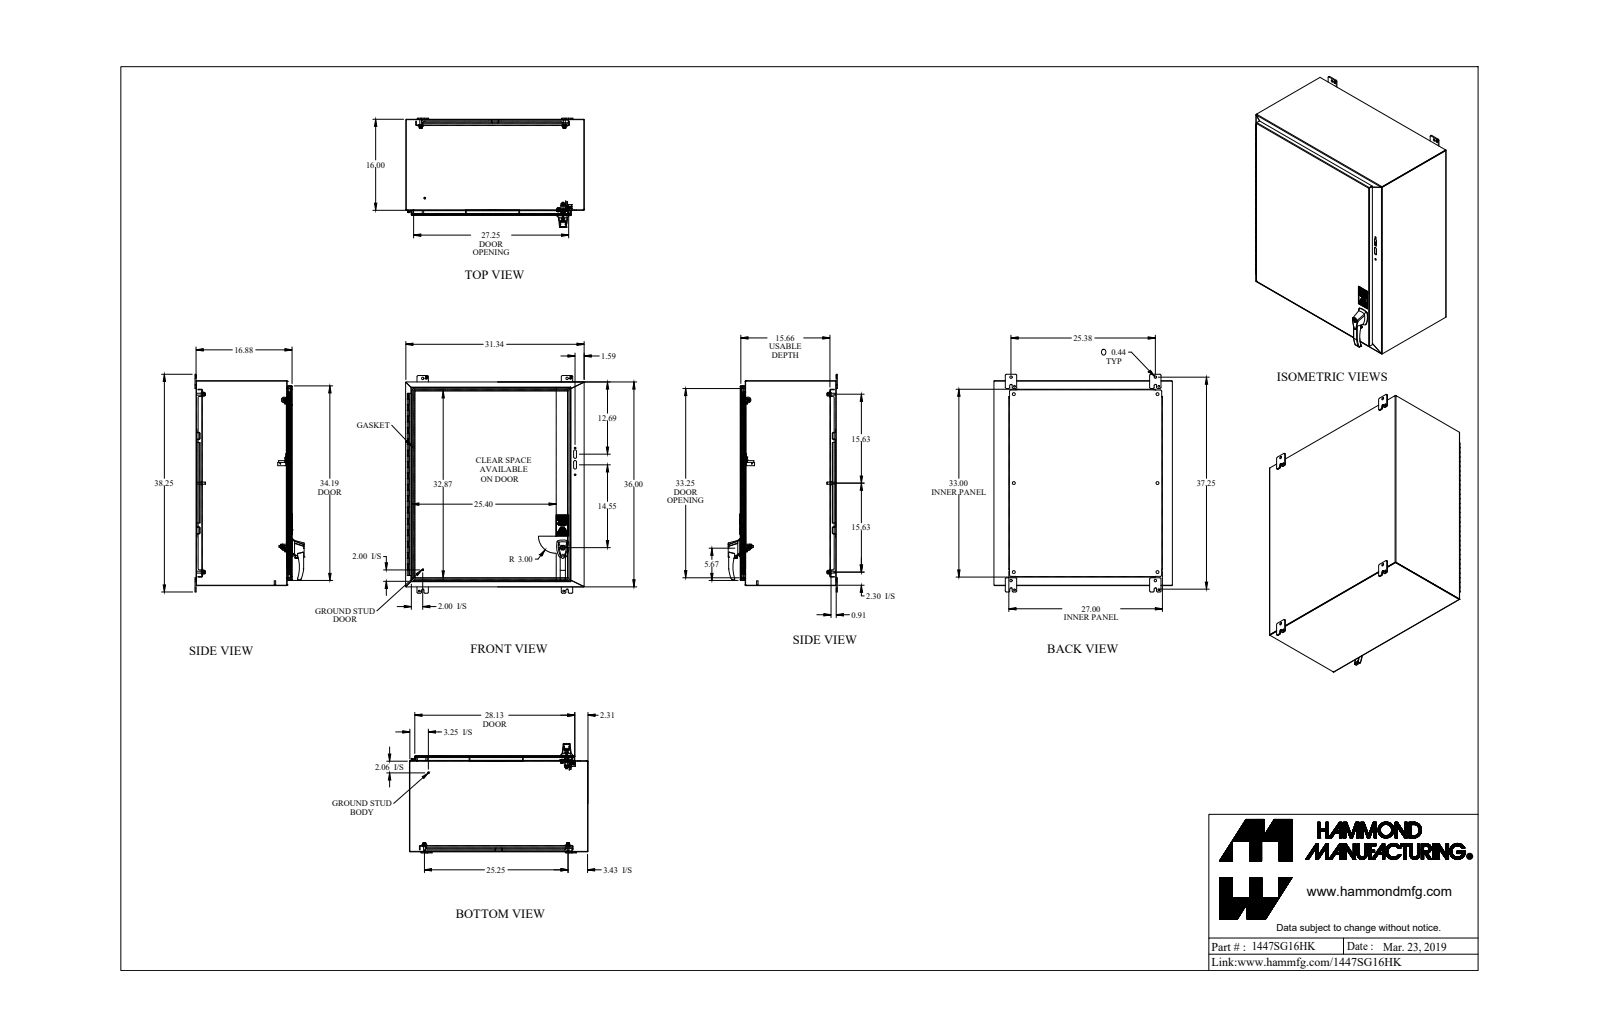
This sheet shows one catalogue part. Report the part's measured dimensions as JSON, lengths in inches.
{"part_name": "1447SG16HK", "step_written_by": "SolidWorks 2019 (AUTOMOTIVE_DESIGN)", "units": "inches", "bodies": {"solids": 60, "faces": 1420, "planar": 890, "cylindrical": 407, "other": 123}, "overall_size": [38.25, 31.375, 19.177], "volume_in3": 476, "surface_area_in2": 12273, "round_holes": [[0.5, 6], [0.313, 5], [0.176, 4], [0.307, 4], [0.437, 4], [0.445, 4], [0.156, 2], [0.173, 2], [0.215, 2], [0.25, 2], [0.265, 2], [0.281, 2]], "round_bosses_or_shafts": [[0.375, 10], [0.25, 7], [1, 6], [0.65, 6], [0.33, 6], [0.156, 4], [0.5, 2], [0.402, 2]], "partial_cylinders_radius": [[0.25, 34], [0.188, 29], [0.036, 18], [0.108, 18], [0.125, 13], [0.116, 12], [0.03, 10], [0.218, 8]], "face_to_face_distances": [0.072, 16.803, 31.303, 16.731, 35.928, 16.875, 0.095, 15.771, 15.699, 1.032], "hole_center_spacings": [25.25, 15.625, 25.375, 29.694, 1.11, 1.735, 1.736, 3.911]}
